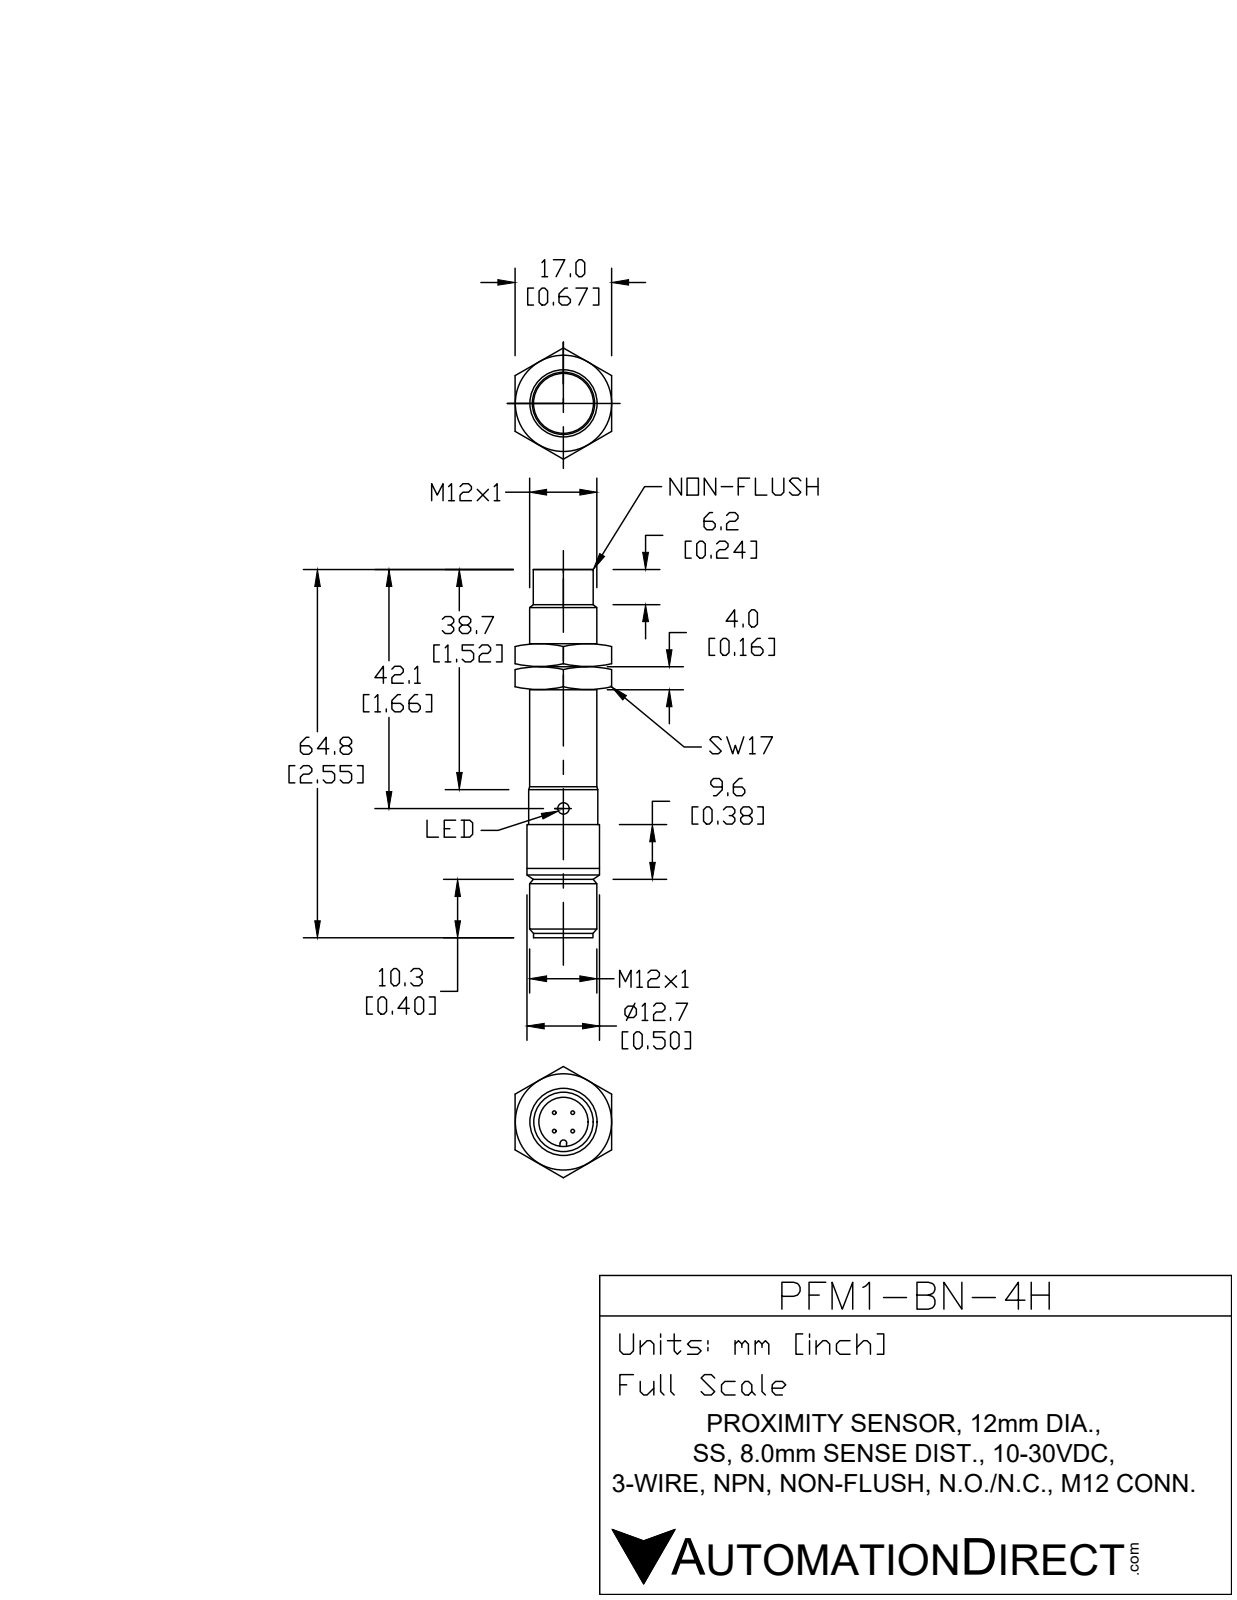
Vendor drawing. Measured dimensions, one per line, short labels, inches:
name: PFM1-BN-4H
written by: SolidWorks 2017 (AUTOMOTIVE_DESIGN)
unit: in
bodies: 4 solids, 73 faces (11 planar, 36 cylindrical, 26 other)
size: 2.543 × 0.5 × 0.5
volume: 0.409 in³; area: 6.284 in²
holes: 1× ⌀0.118, 1× ⌀0.331, 1× ⌀0.335, 1× ⌀0.374
bosses: 4× ⌀0.039, 1× ⌀0.5, 1× ⌀0.472, 1× ⌀0.413, 1× ⌀0.394, 1× ⌀0.37
rounds: 1× R0.024, 1× R0.219
face distances: 1.839, 1.909, 0.071, 0.236, 2.075, 2.146, 2.193, 1.957, 0.118, 0.047
